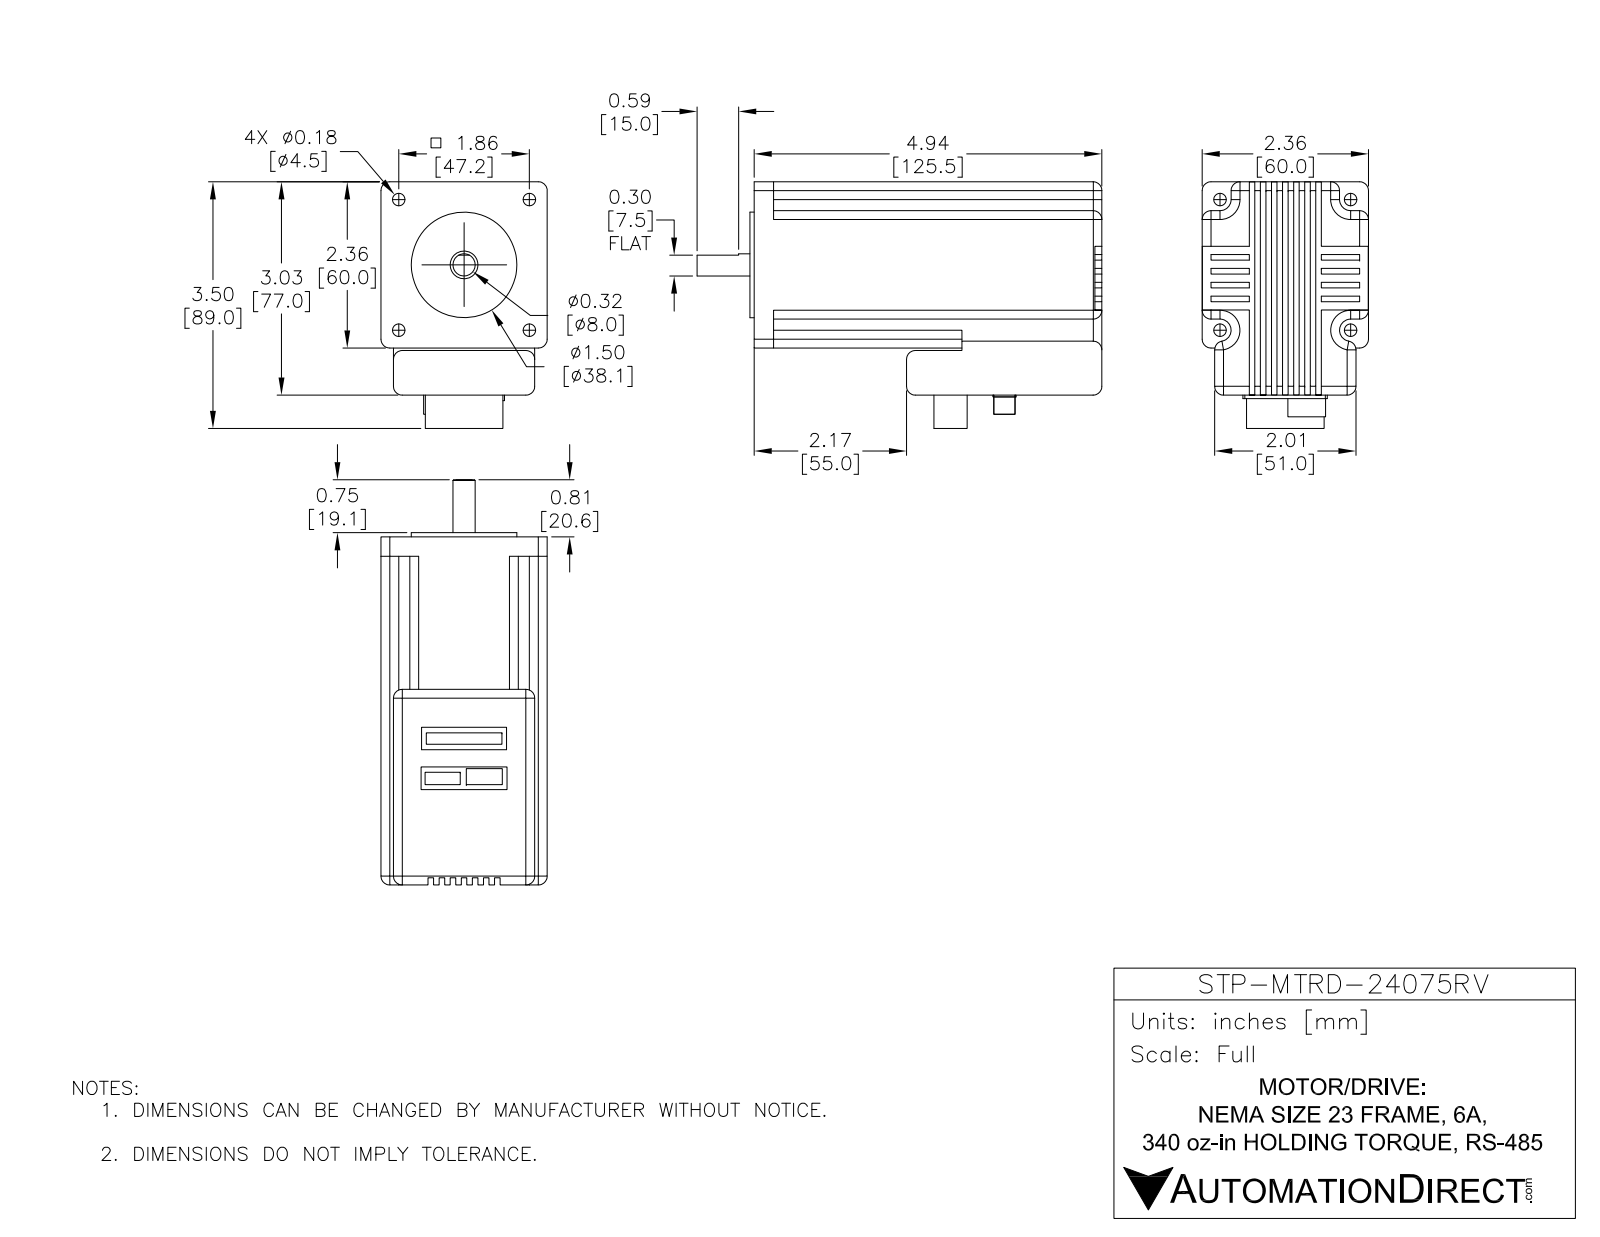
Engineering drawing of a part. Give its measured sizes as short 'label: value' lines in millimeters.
name: STP-MTRD-24075RV
written by: SolidWorks 2017 (AUTOMOTIVE_DESIGN)
unit: mm
bodies: 1 solid, 693 faces (261 planar, 292 cylindrical, 140 other)
size: 146.2 × 78.25 × 60
volume: 447 302 mm³; area: 50 381 mm²
holes: 4× ⌀4.5, 1× ⌀10, 1× ⌀19
bosses: 4× ⌀5.5, 2× ⌀5.6, 1× ⌀38.1, 1× ⌀8
rounds: 122× R0.5, 28× R3.2, 7× R0.67, 6× R2.5, 4× R4, 4× R10.96, 3× R0.67, 3× R0.68
face distances: 60, 2, 4, 6, 10, 8, 12, 17, 10.43, 49.57
hole spacings: 33.33, 47.14, 33.19, 33.47, 66.67
